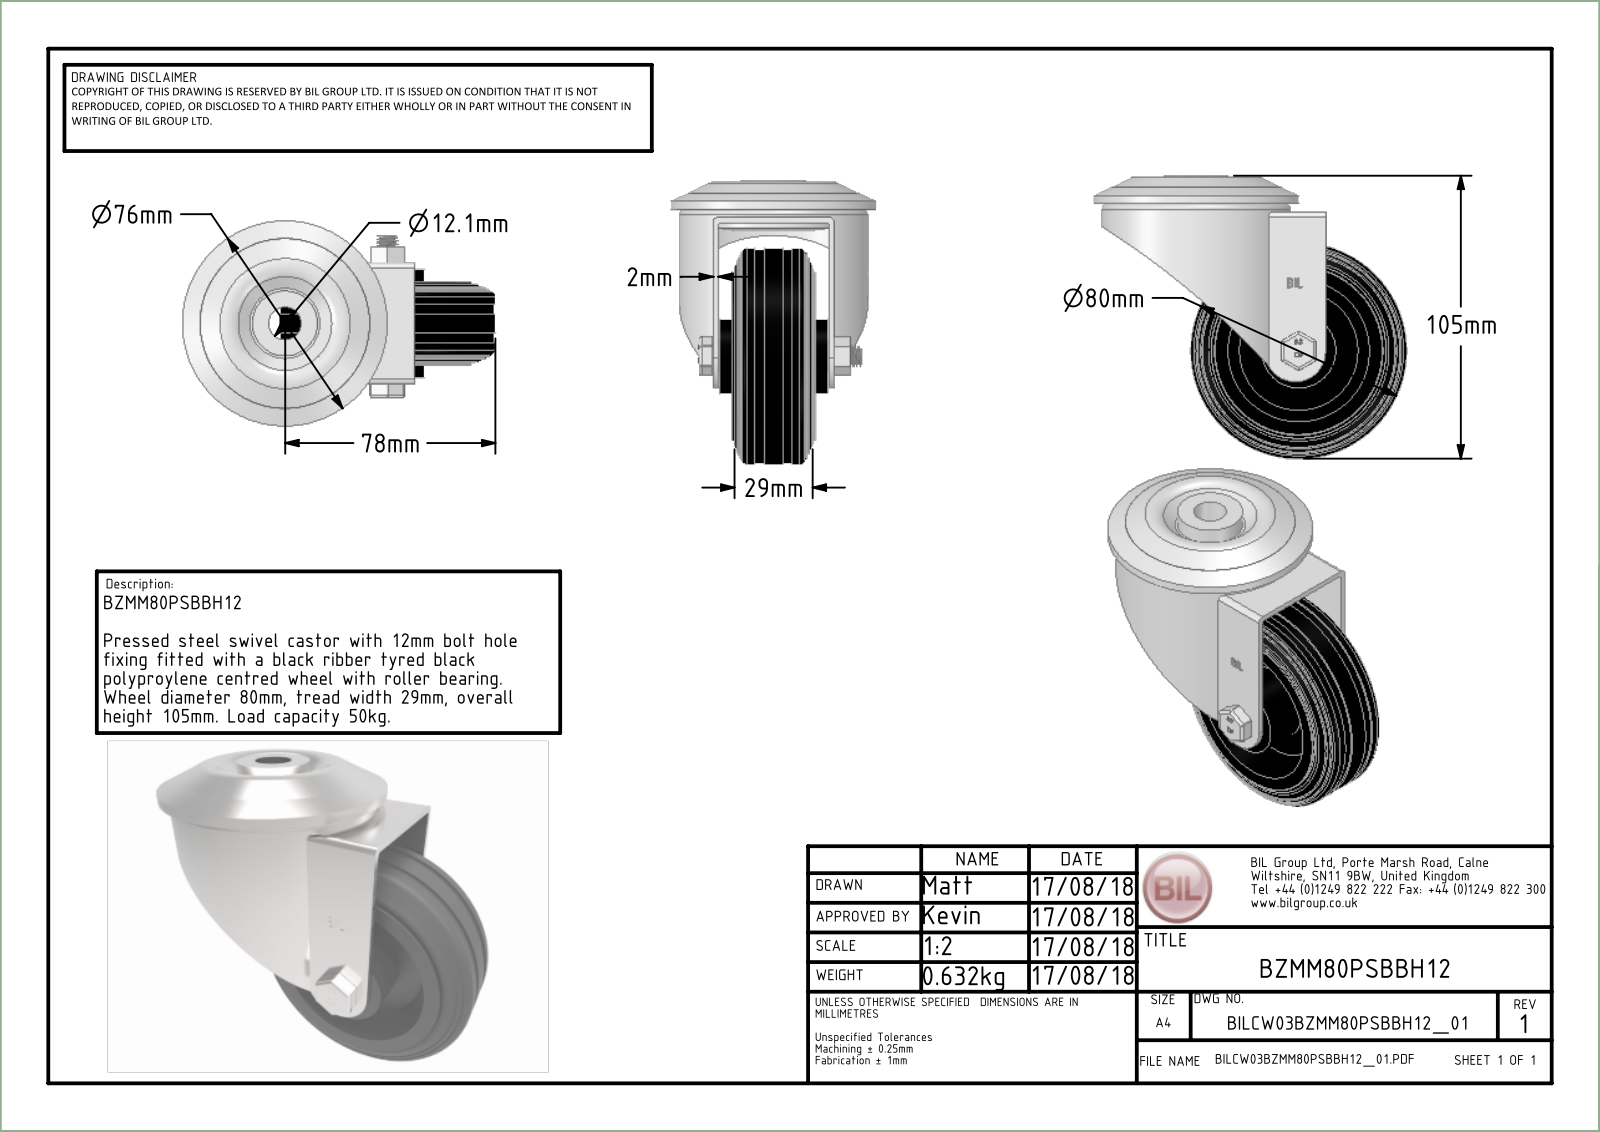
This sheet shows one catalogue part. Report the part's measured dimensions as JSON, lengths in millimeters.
{"part_name": "BZMM80PSBBH12 v3; BZMM80ASBH12 v1; ZINC PLATED, PRESSED STEEL FORKS; ZINC PLATED, PRESSED STEEL TOP PLATE (+8 more)", "step_written_by": "Autodesk Translation Framework v13.20.0.188 (AP242_MANAGED_MODEL_BASED_3D_ENGINEERING_MIM_LF)", "units": "millimeters", "bodies": {"solids": 18, "faces": 482, "planar": 182, "cylindrical": 164, "other": 136}, "overall_size": [116, 105, 76], "volume_mm3": 168178, "surface_area_mm2": 91071, "round_holes": [[0.66, 2], [12.2, 2], [8, 1], [8.2, 1], [8.4, 1], [8.6, 1], [12.5, 1], [20, 1], [25, 1], [48.32, 1], [51, 1], [55, 1]], "round_bosses_or_shafts": [[3.75, 8], [70, 1], [61, 1], [49.5, 1], [38, 1], [24.9, 1], [24, 1], [21.31, 1]], "partial_cylinders_radius": [[0.5, 18], [0.25, 12], [0.33, 4], [0.64, 4], [1.25, 4], [0.63, 2], [0.64, 2], [2.5, 2]], "face_to_face_distances": [17.25, 5.5, 2.5, 8, 42.5, 34.5, 37, 25.25, 19.75, 22.75], "hole_center_spacings": [3.22, 2.49]}
